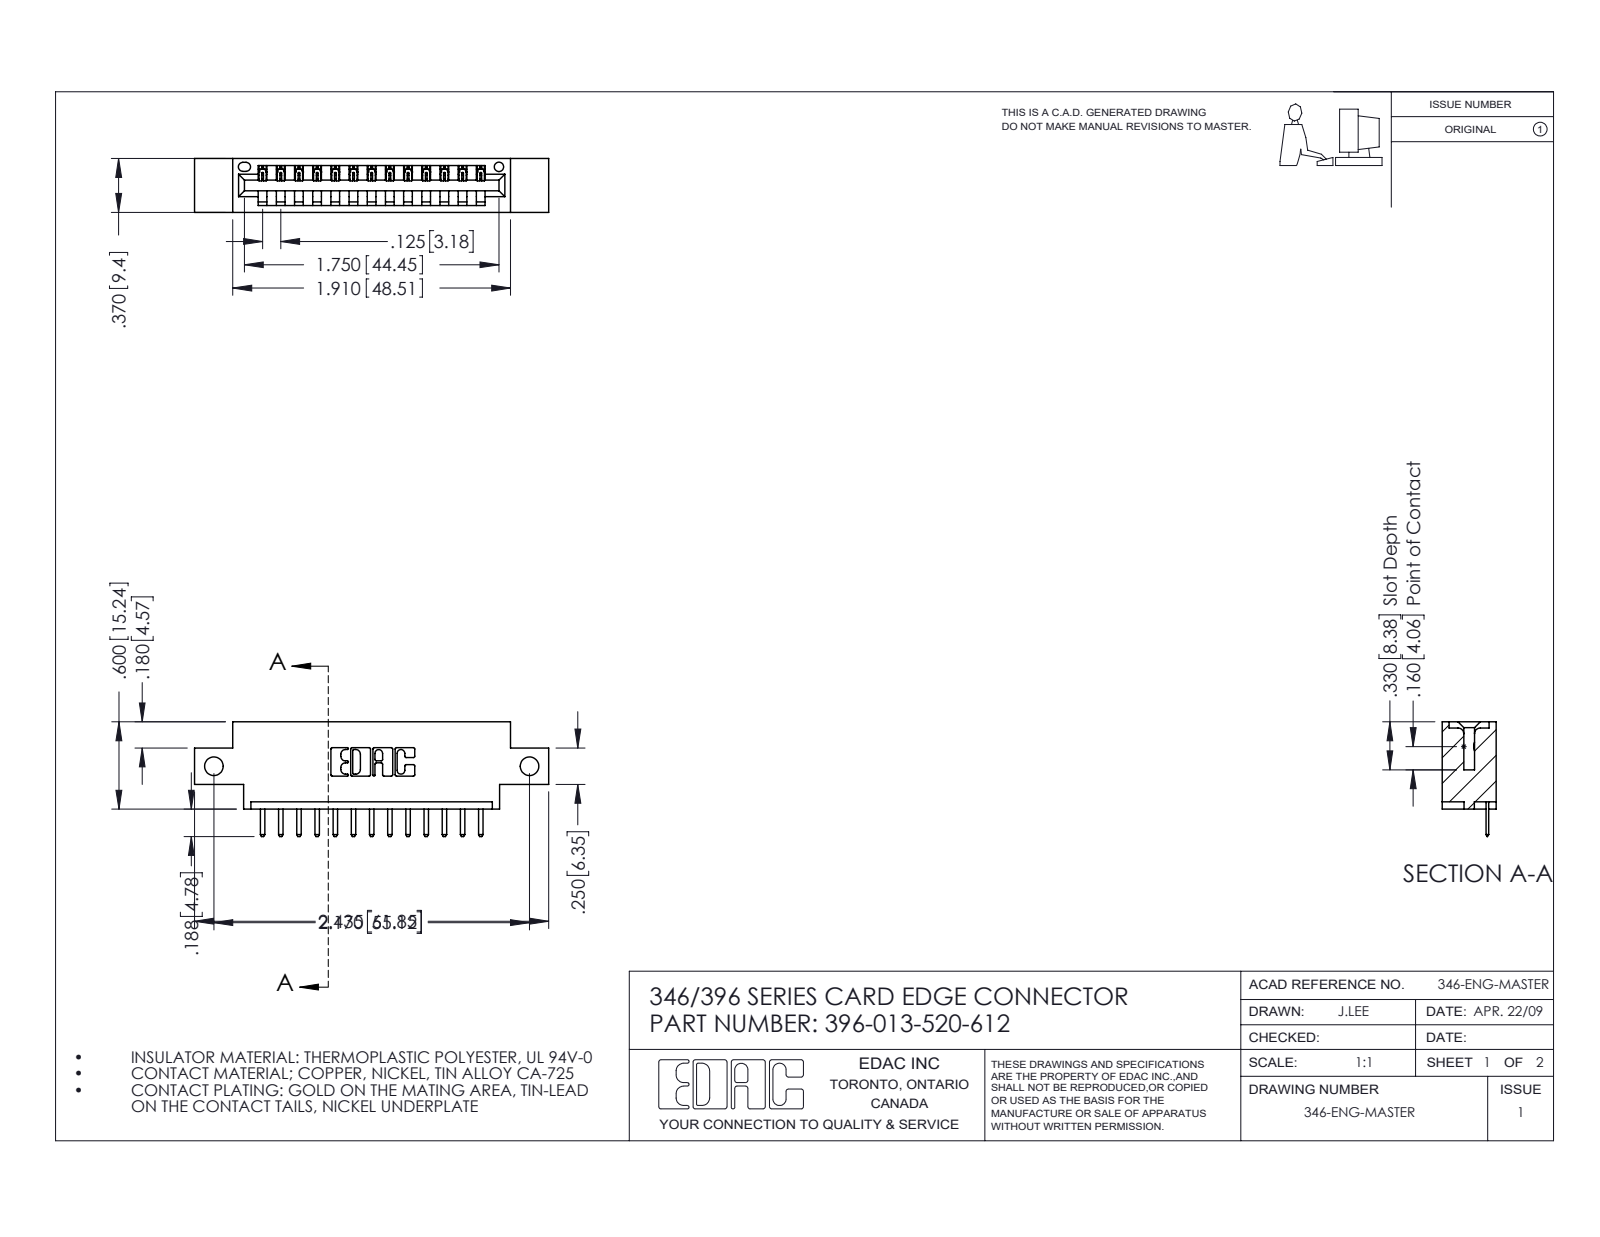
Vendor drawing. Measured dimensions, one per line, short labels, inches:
name: 396-013-520-612; 345-292-001_345-293-120; 346 Part_0.170 Offset - Side Mount
written by: SolidWorks 2016 (CONFIG_CONTROL_DESIGN)
unit: in
bodies: 14 solids, 932 faces (626 planar, 306 cylindrical, 0 other)
size: 2.435 × 0.788 × 0.37
volume: 0.332 in³; area: 9.885 in²
holes: 2× ⌀0.128, 1× ⌀0.064
rounds: 28× R0.01, 26× R0.006, 22× R0.01, 6× R0.007, 6× R0.031, 3× R0.026, 2× R0.031, 2× R0.04
face distances: 0.37, 0.25, 0.048, 0.322, 0.148, 0.222, 0.1, 0.174, 0.072, 0.298
hole spacings: 2.17
